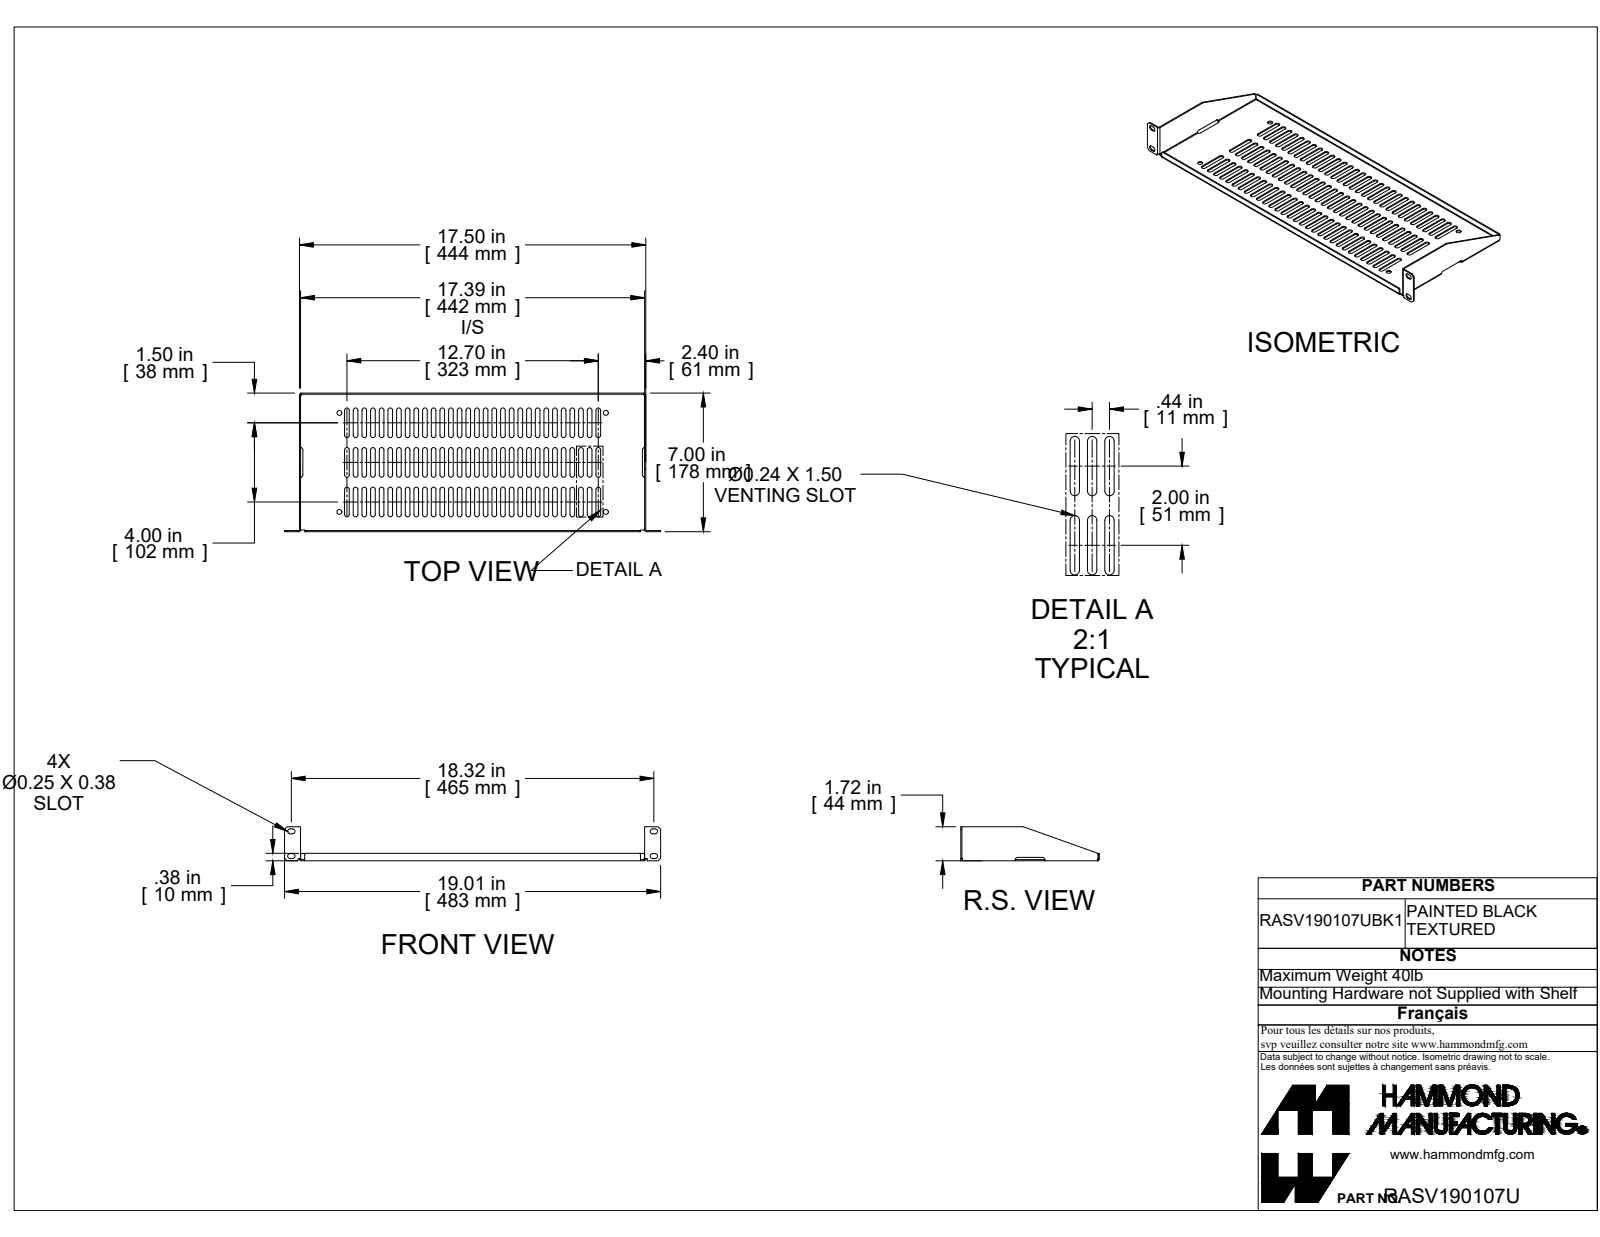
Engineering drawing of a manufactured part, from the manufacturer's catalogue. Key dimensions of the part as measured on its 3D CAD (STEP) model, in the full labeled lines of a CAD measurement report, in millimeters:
Part name (STEP PRODUCT): RASV190107UBK1_REV4
STEP written by: SolidWorks 2021 (AUTOMOTIVE_DESIGN)
Units: millimetres
Bodies: 1 solid, 463 faces (247 planar, 216 cylindrical, 0 other)
Overall size (bounding box): 483.2 × 177.8 × 43.6
Volume: 113 000 mm³ · Surface area: 169 400 mm²
Round holes (diameter × count): ⌀6.4 ×4
Partial cylindrical surfaces — rounded edges, fillets, slot ends (radius × count): R3 ×174, R3.2 ×14, R2.2 ×6, R3 ×6, R0.7 ×4, R0.7 ×2
Main face-to-face distances: 1.4, 443.6, 176.4, 442.1, 445, 177.8, 174.9, 22.3, 8.1, 9.6
Hole centre spacings: 127, 342.1, 364.9
